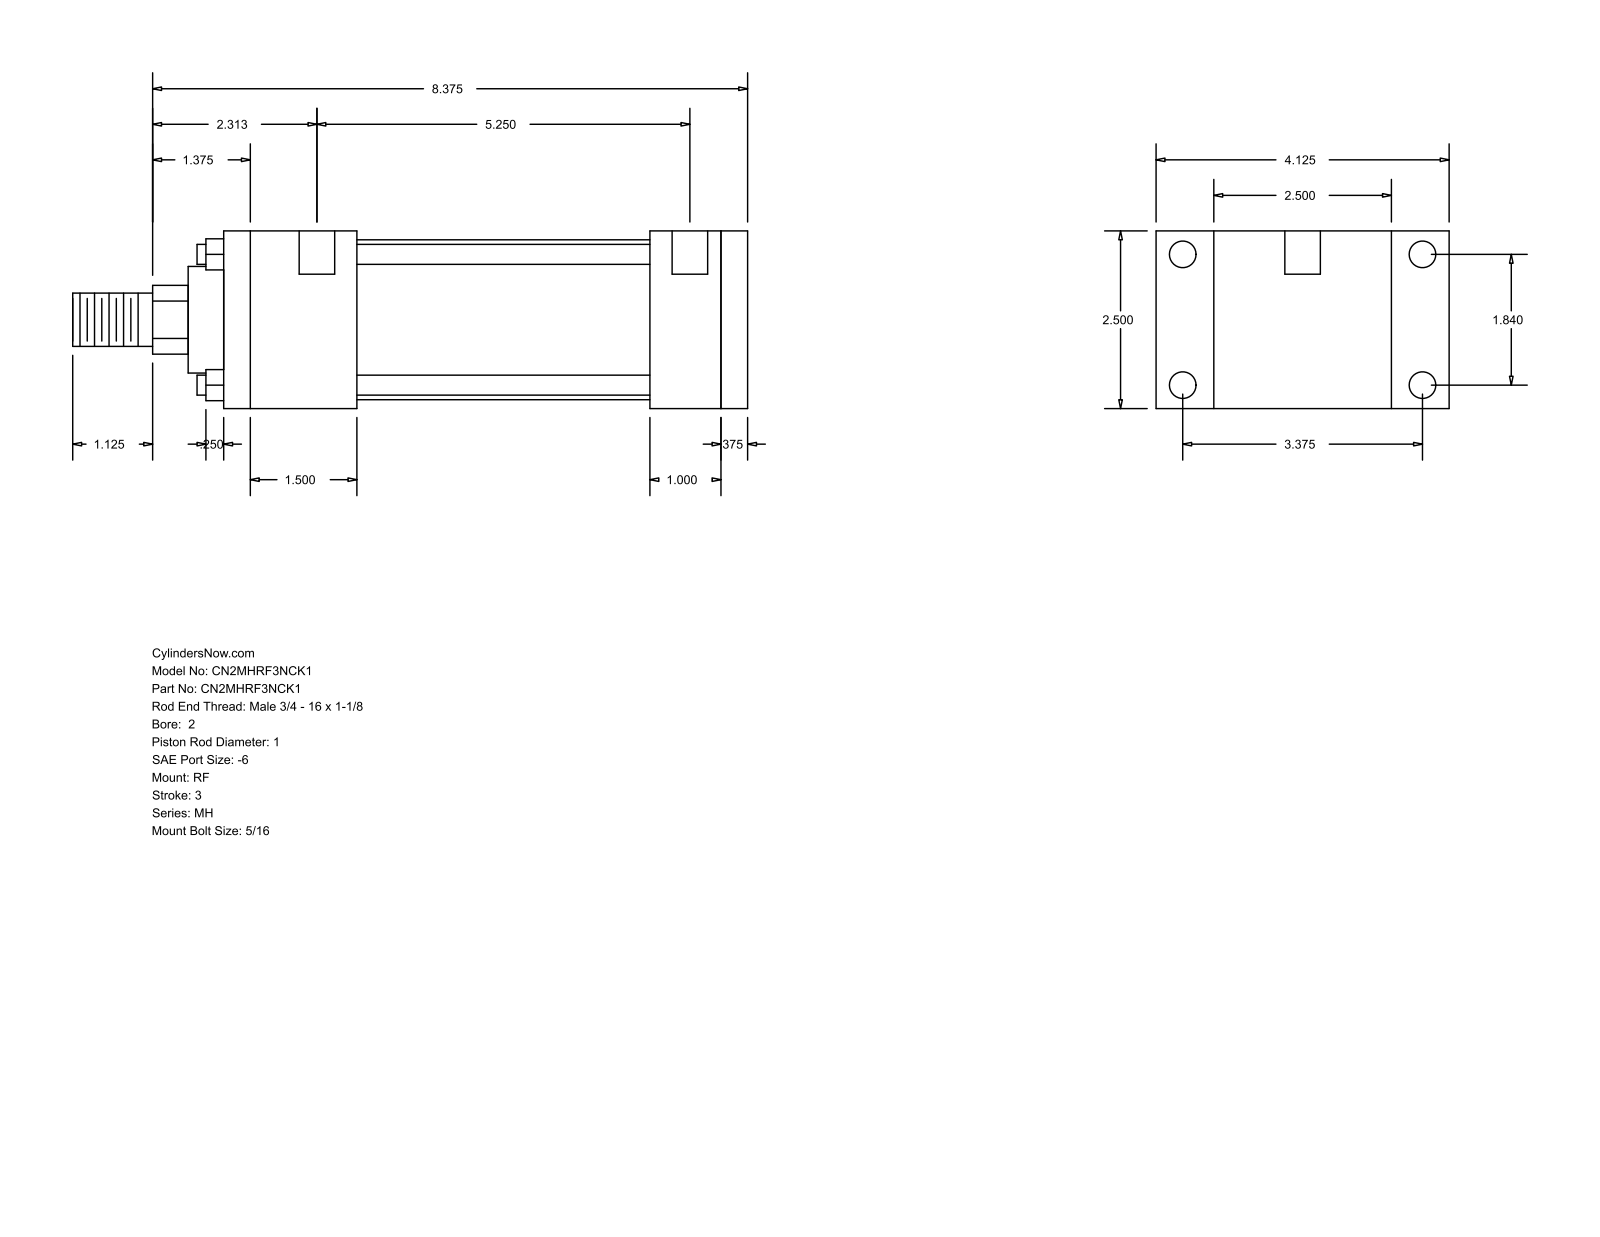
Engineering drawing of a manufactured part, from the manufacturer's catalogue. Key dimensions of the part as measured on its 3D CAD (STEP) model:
Part name (STEP PRODUCT): MH_RF__0200_1
STEP written by: GSSL Pune (CONFIG_CONTROL_DESIGN)
Units: millimetres
Bodies: 0 solids, 92 faces (64 planar, 28 cylindrical, 0 other)
Overall size (bounding box): 241.3 × 104.78 × 63.5
Round holes (diameter × count): ⌀5.56 ×4, ⌀9.53 ×4, ⌀12.7 ×2
Round bosses / shafts (diameter × count): ⌀7.14 ×4, ⌀57.15 ×1, ⌀38.1 ×1, ⌀25.4 ×1, ⌀19.05 ×1
Partial cylindrical surfaces — rounded edges, fillets, slot ends (radius × count): R12.29 ×1
Main face-to-face distances: 63.5, 187.32, 9.52, 177.8, 20.64, 25.4, 47.63, 152.4, 104.77, 130.17
Hole centre spacings: 46.74, 85.72, 97.63, 141.28, 3.17, 4.76, 133.35, 136.52
